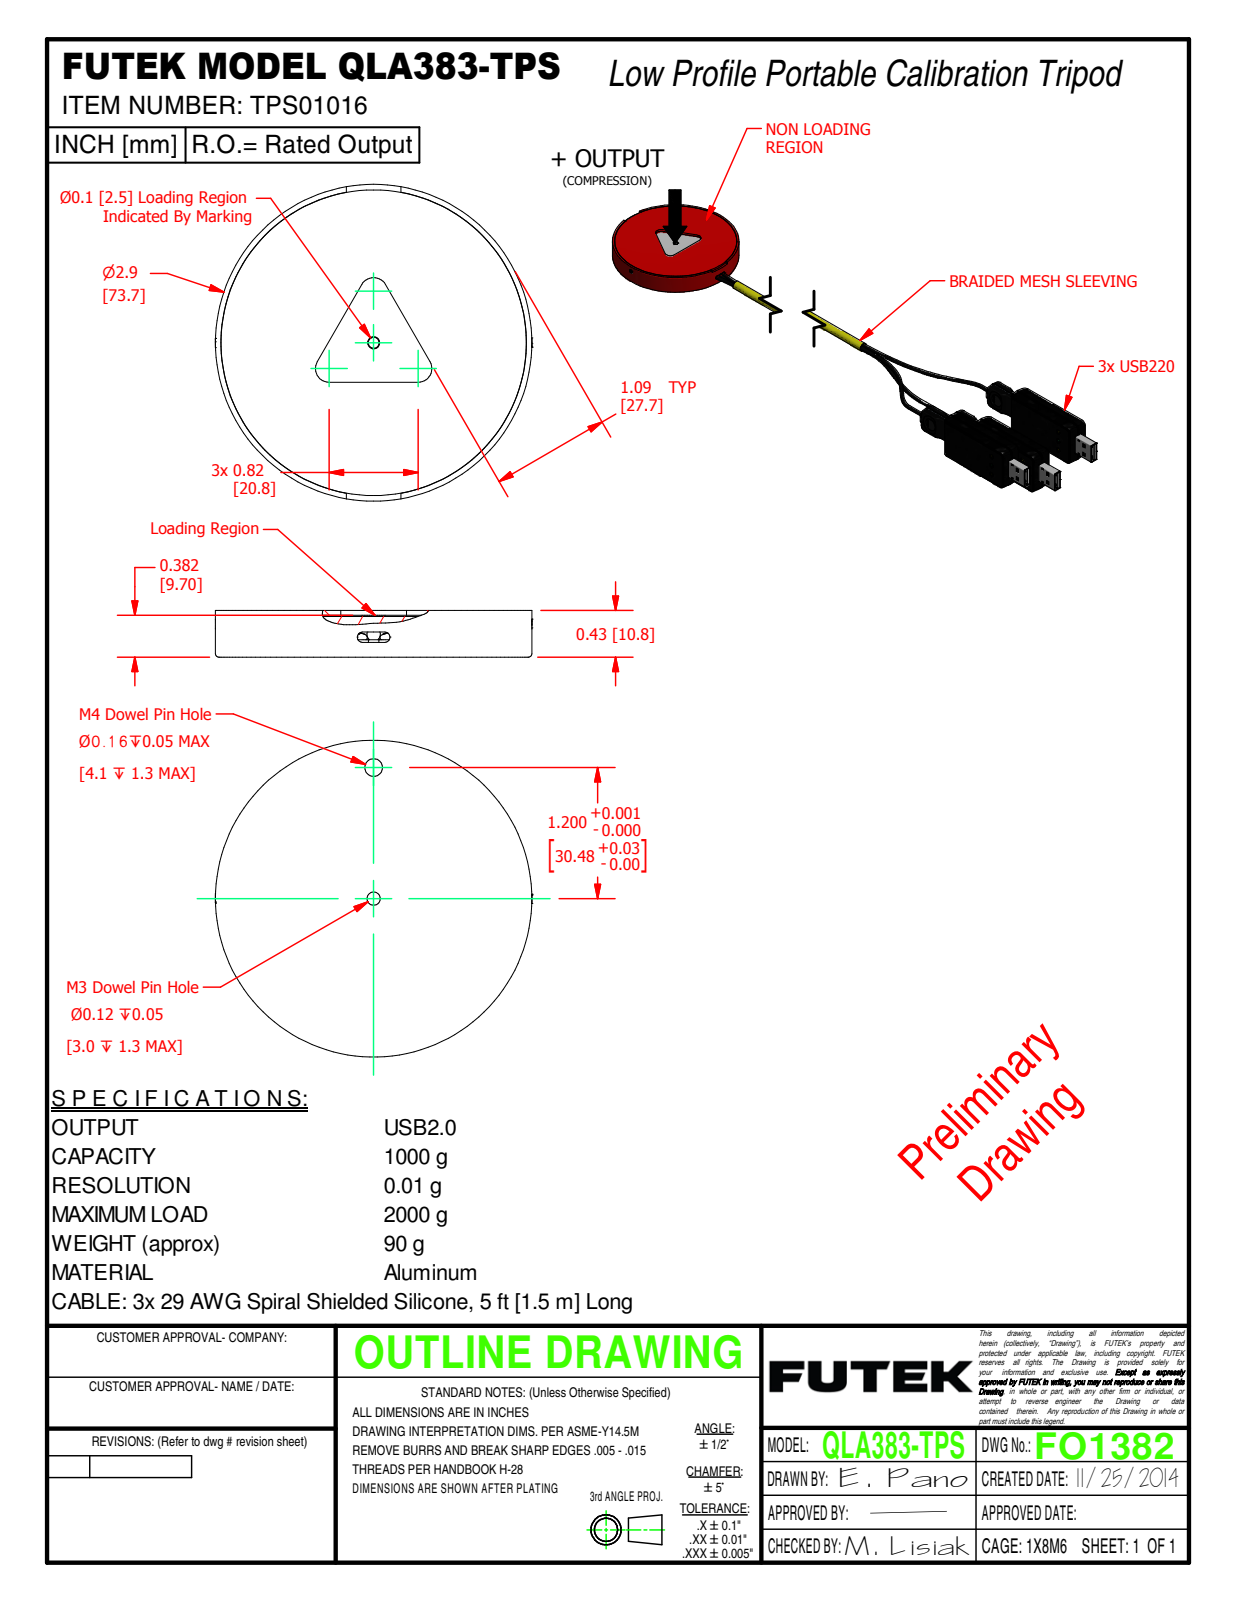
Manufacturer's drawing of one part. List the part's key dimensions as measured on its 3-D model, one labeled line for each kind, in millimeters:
Part name (STEP PRODUCT): QLA383_Shrinkwrap
STEP written by: Autodesk Inventor 2014 (CONFIG_CONTROL_DESIGN)
Units: millimetres
Bodies: 0 solids, 44 faces (27 planar, 12 cylindrical, 5 other)
Overall size (bounding box): 73.66 × 73.66 × 10.85
Round holes (diameter × count): ⌀3.05 ×1, ⌀4.09 ×1, ⌀68.58 ×1
Round bosses / shafts (diameter × count): ⌀73.66 ×1, ⌀71.07 ×1
Partial cylindrical surfaces — rounded edges, fillets, slot ends (radius × count): R1.19 ×4, R3.17 ×3
Main face-to-face distances: 10.85, 3.43, 7.42, 9.7, 6.27, 1.15, 9.44, 6.01, 1.41, 6.13
Hole centre spacings: 30.48
